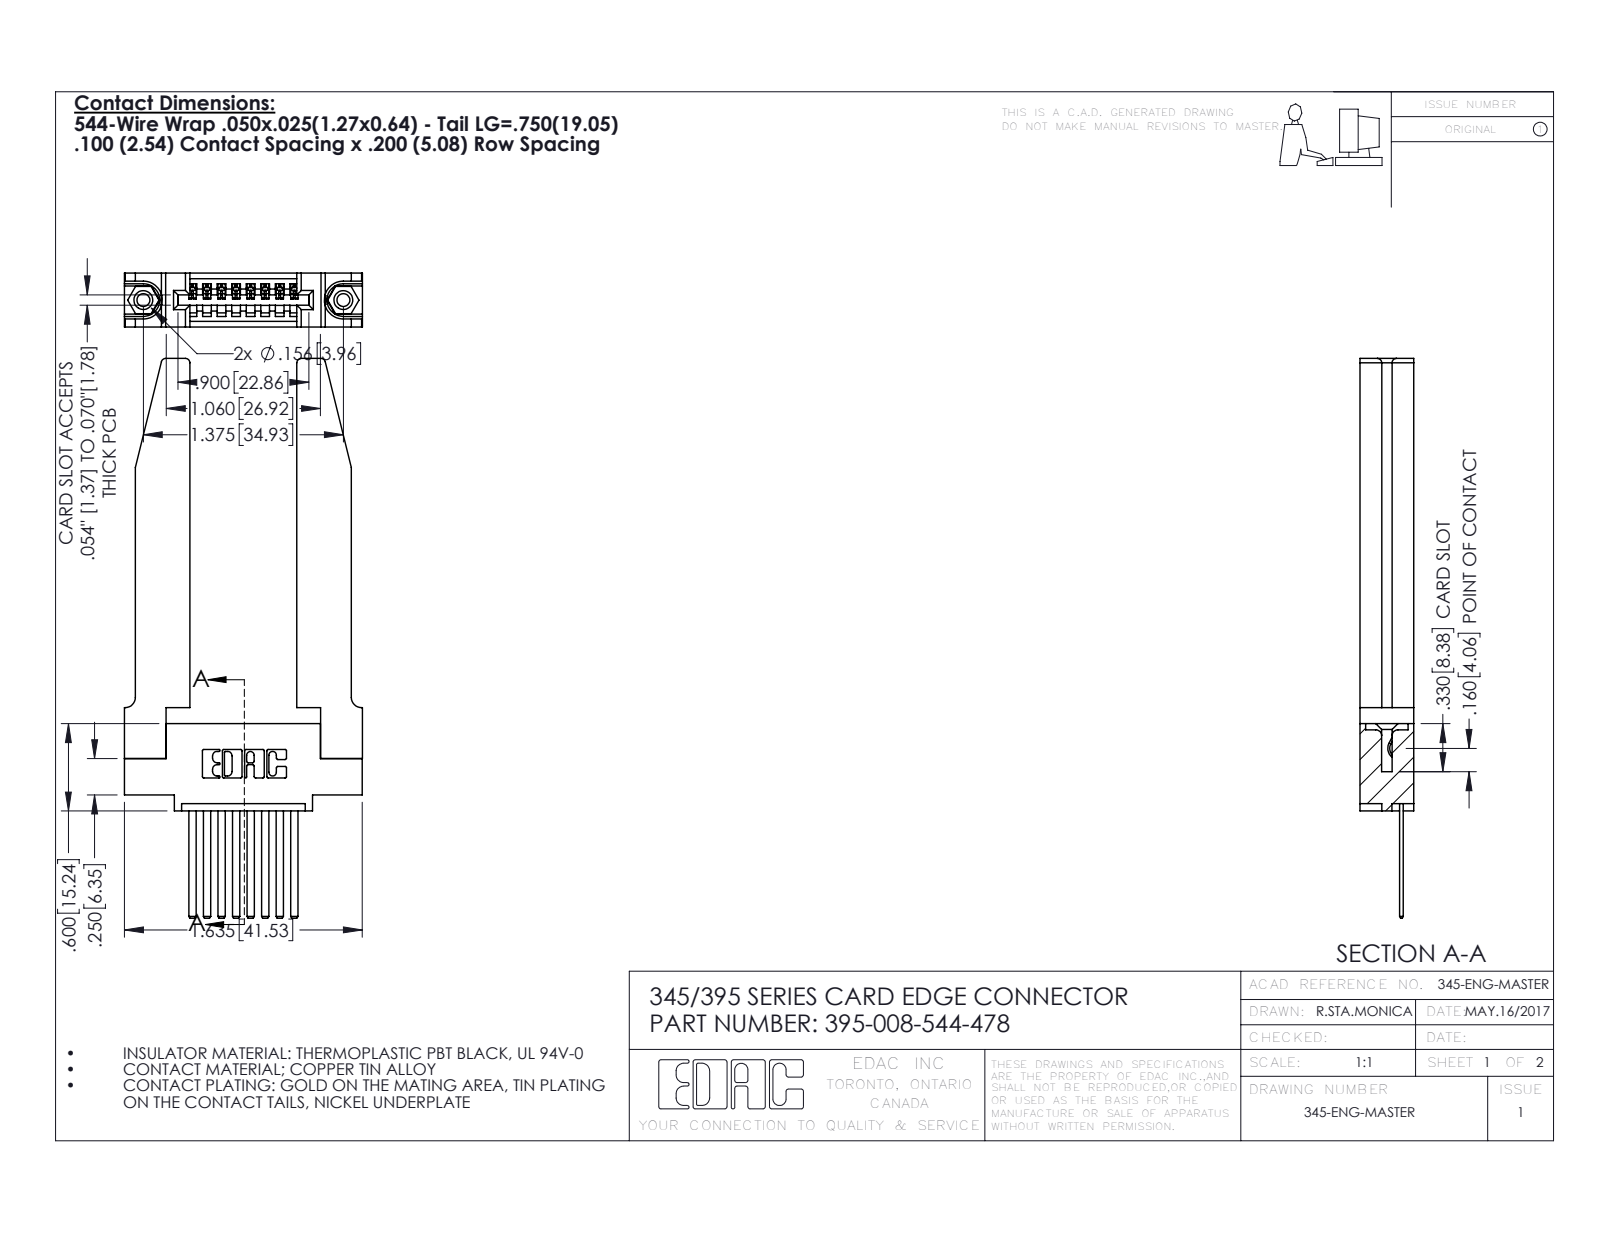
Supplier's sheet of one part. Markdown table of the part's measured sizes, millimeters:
| quantity | value |
| --- | --- |
| part name | 345-292-001_345-293-144; 345 Part_0.110 Offset - 0.156 Dia-TH; 345-220-078_345-220-078; 395-008-544-478 (+1 more) |
| STEP written by | SolidWorks 2016 (CONFIG_CONTROL_DESIGN) |
| units | millimeters |
| bodies | 13 solids, 780 faces (514 planar, 214 cylindrical, 52 other) |
| overall size | 97.7 × 41.6 × 9.4 |
| volume | 11 500 mm³ |
| surface area | 11 650 mm² |
| round holes (diameter × count) | 2.3 × 2, 3.2 × 2, 4 × 2, 1.6 × 1 |
| round bosses / shafts (diameter × count) | 3.9 × 2 |
| partial cylindrical surfaces (radius × count) | 0.3 × 22, 0.2 × 16, 0.8 × 8, 0.2 × 6, 0.8 × 6, 0.7 × 3, 0.8 × 2, 1 × 2 |
| main face-to-face distances | 9.4, 1.8, 7.6, 3.8, 5.6, 3.8, 18.7, 2, 2.5, 6.9 |
| hole center spacings | 6.9, 29.1, 34.9 |
